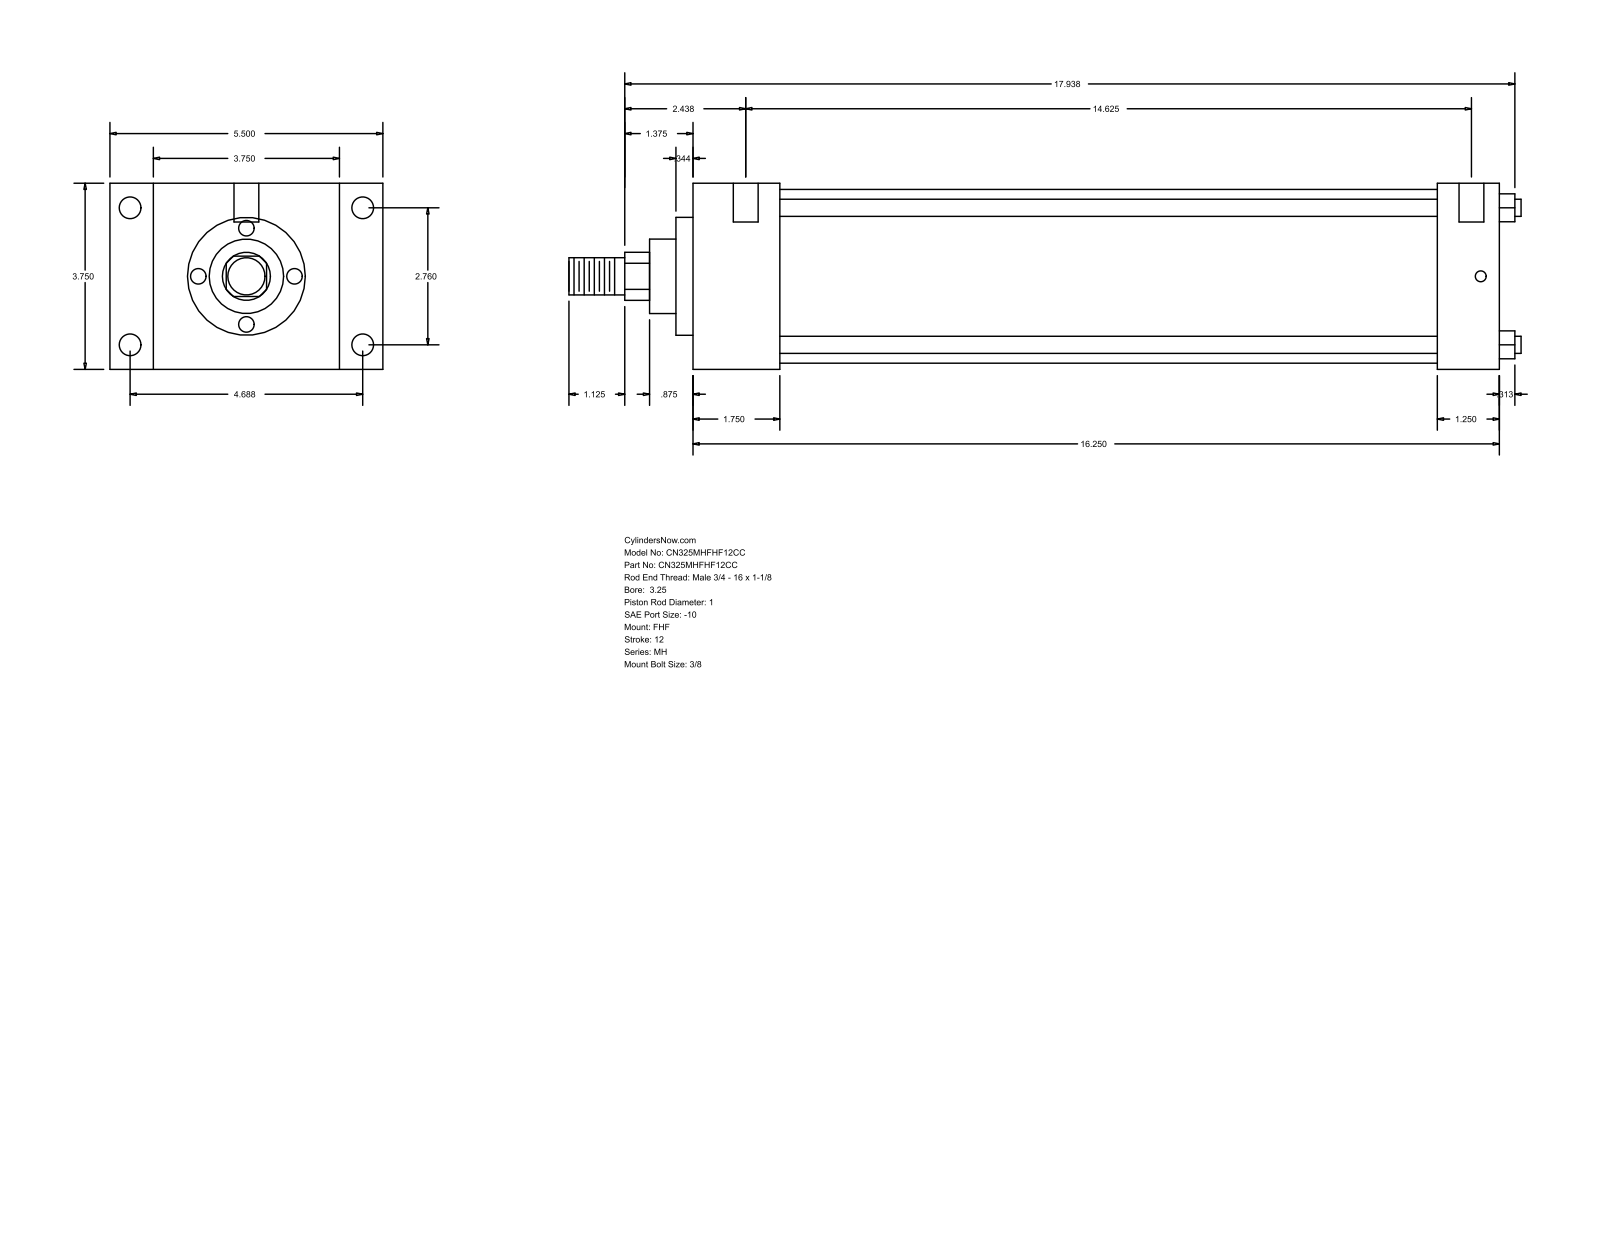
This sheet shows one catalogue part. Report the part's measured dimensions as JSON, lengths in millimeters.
{"part_name": "MH_FHF__0325_1", "step_written_by": "GSSL Pune (CONFIG_CONTROL_DESIGN)", "units": "millimeters", "bodies": {"solids": 0, "faces": 90, "planar": 61, "cylindrical": 29, "other": 0}, "overall_size": [487.36, 139.7, 95.25], "round_holes": [[5.56, 4], [11.13, 4], [12.7, 2]], "round_bosses_or_shafts": [[8.76, 4], [88.9, 1], [60.33, 1], [38.1, 1], [25.4, 1], [19.05, 1]], "partial_cylinders_radius": [[12.29, 1]], "face_to_face_distances": [95.24, 412.76, 44.46, 368.3, 22.23, 117.47, 139.7, 381.01, 336.55, 31.75], "hole_center_spacings": [70.1, 119.06, 138.16, 377.82, 1.58, 4.76, 371.48, 373.06]}
